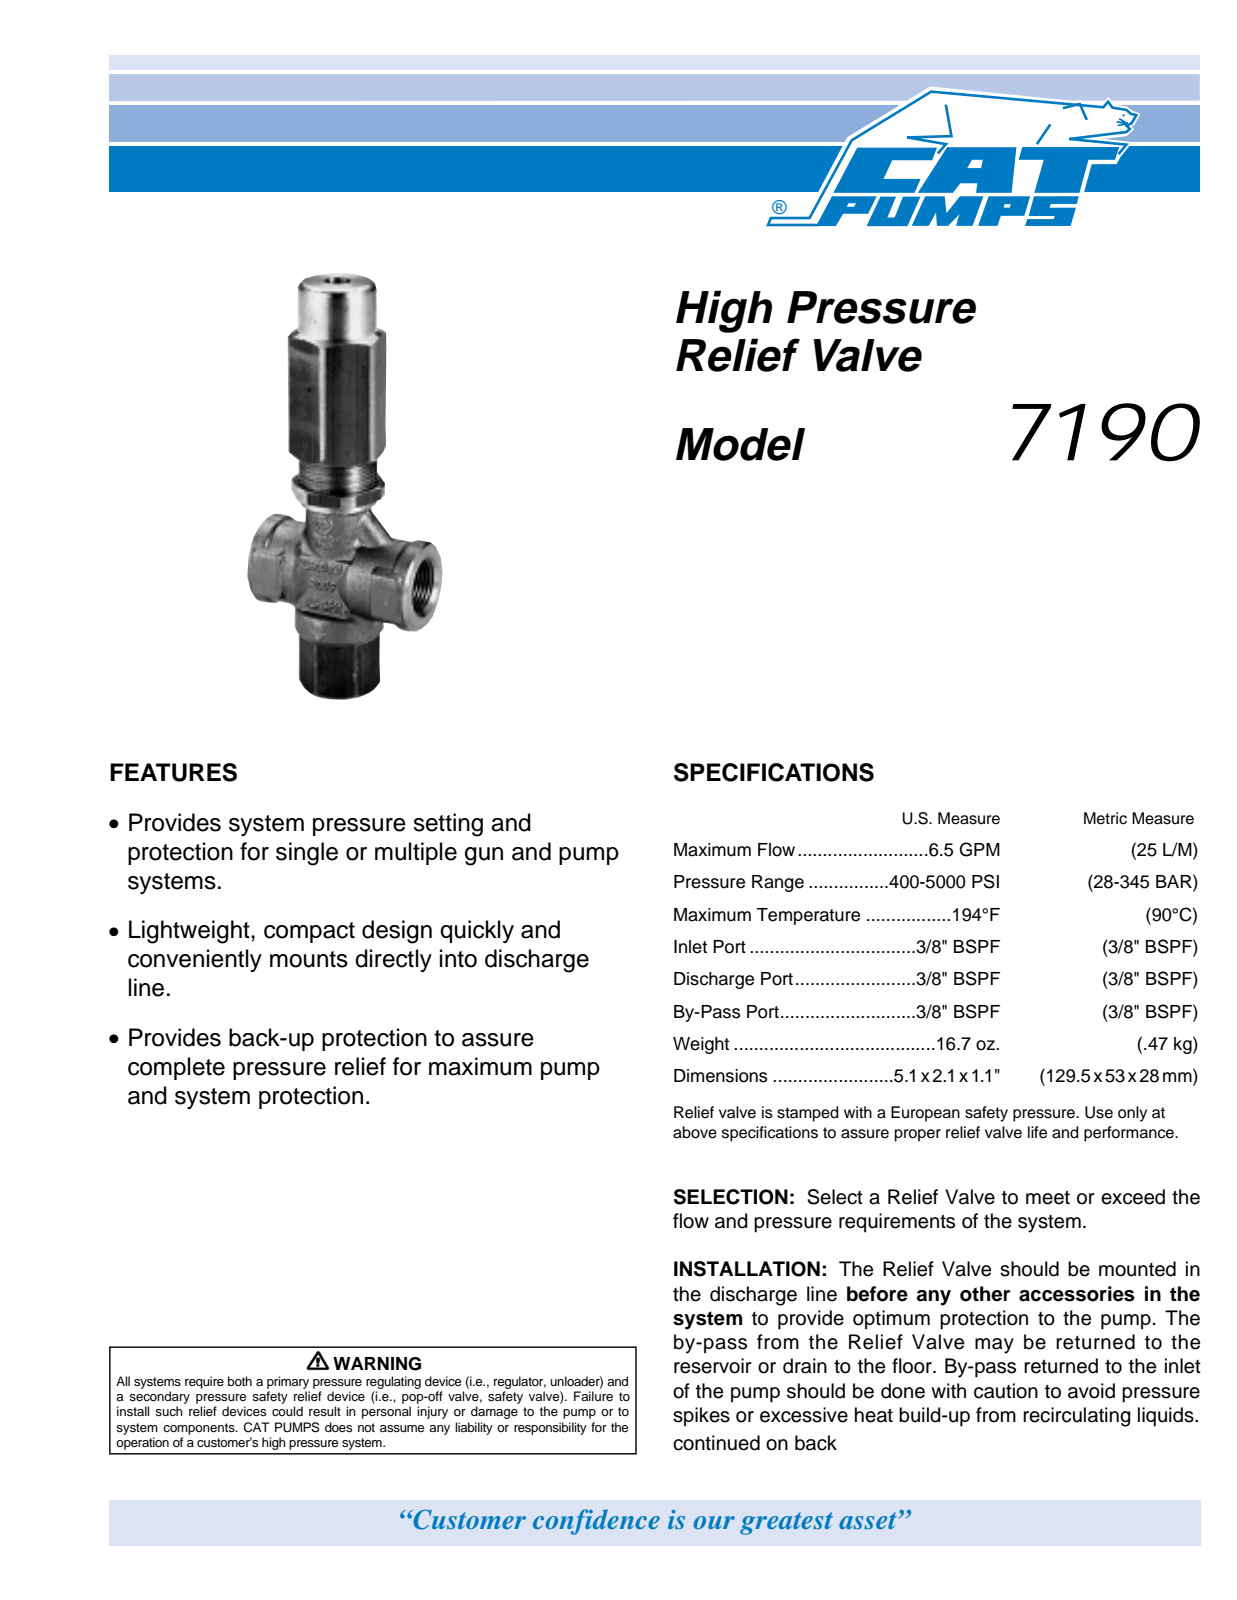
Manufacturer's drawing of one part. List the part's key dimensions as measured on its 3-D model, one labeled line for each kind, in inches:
Part name (STEP PRODUCT): 7190
STEP written by: SolidWorks 2017 (CONFIG_CONTROL_DESIGN)
Units: inches
Bodies: 1 solid, 142 faces (85 planar, 37 cylindrical, 20 other)
Overall size (bounding box): 5.1 × 2 × 1.177
Volume: 4.422 in³ · Surface area: 27.98 in²
Round holes (diameter × count): ⌀0.562 ×2
Round bosses / shafts (diameter × count): ⌀1.08 ×1, ⌀1.075 ×1, ⌀1 ×1, ⌀0.945 ×1, ⌀0.8 ×1
Partial cylindrical surfaces — rounded edges, fillets, slot ends (radius × count): R0.57 ×1, R0.589 ×1
Main face-to-face distances: 1.06, 0.1, 0.96, 0.47, 1.53, 0.86, 0.068, 1.013, 0.57, 1.43
